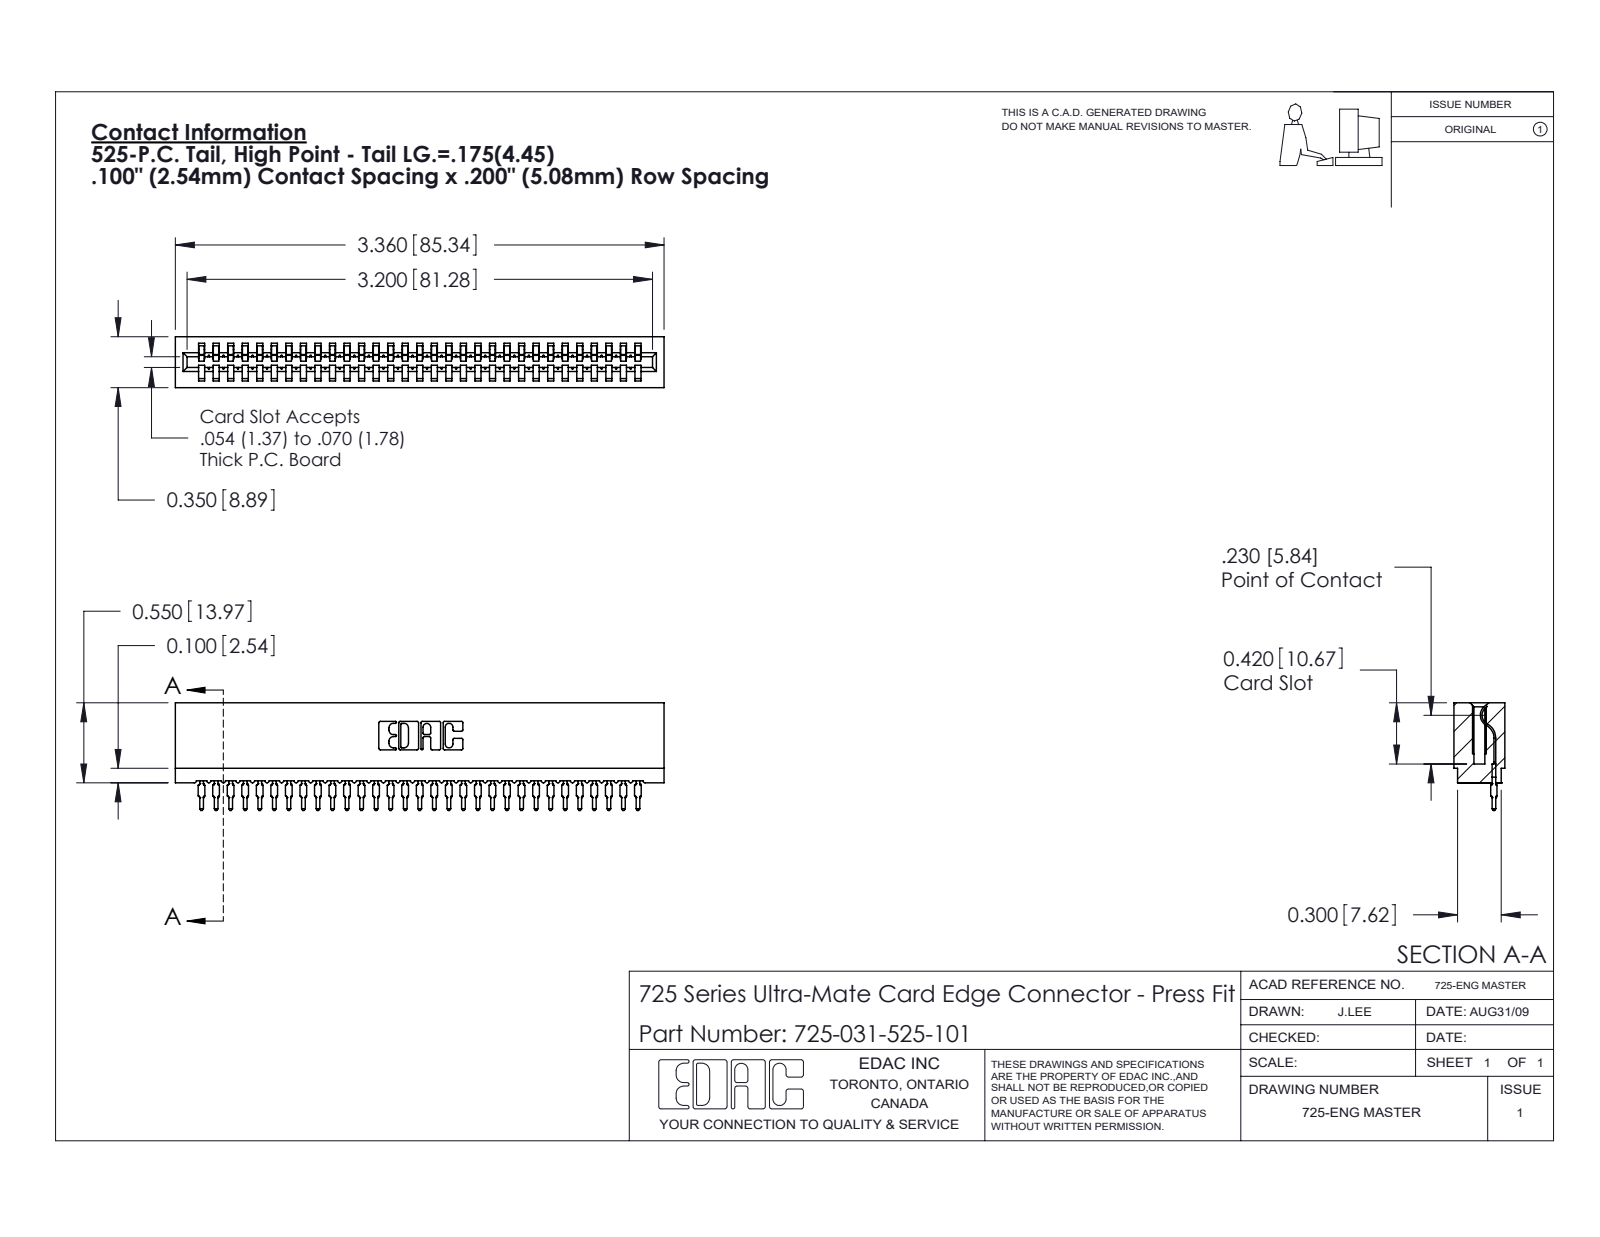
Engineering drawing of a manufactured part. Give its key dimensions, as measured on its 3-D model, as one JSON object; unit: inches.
{"part_name": "745-292-001_525; 725 Part_Insulator Option - 01; 725-031-525-101", "step_written_by": "SolidWorks 2020 (CONFIG_CONTROL_DESIGN)", "units": "inches", "bodies": {"solids": 32, "faces": 3567, "planar": 2132, "cylindrical": 629, "other": 806}, "overall_size": [3.36, 0.741, 0.35], "volume_in3": 0.397, "surface_area_in2": 19.02, "partial_cylinders_radius": [[0.015, 62], [0.021, 62], [0.01, 22], [0.007, 6], [0.031, 6], [0.005, 4], [0.011, 4], [0.026, 3]], "face_to_face_distances": [0.2, 0.1, 0.35, 0.3, 0.4, 0.212, 0.138, 0.5, 0.6, 0.045]}
